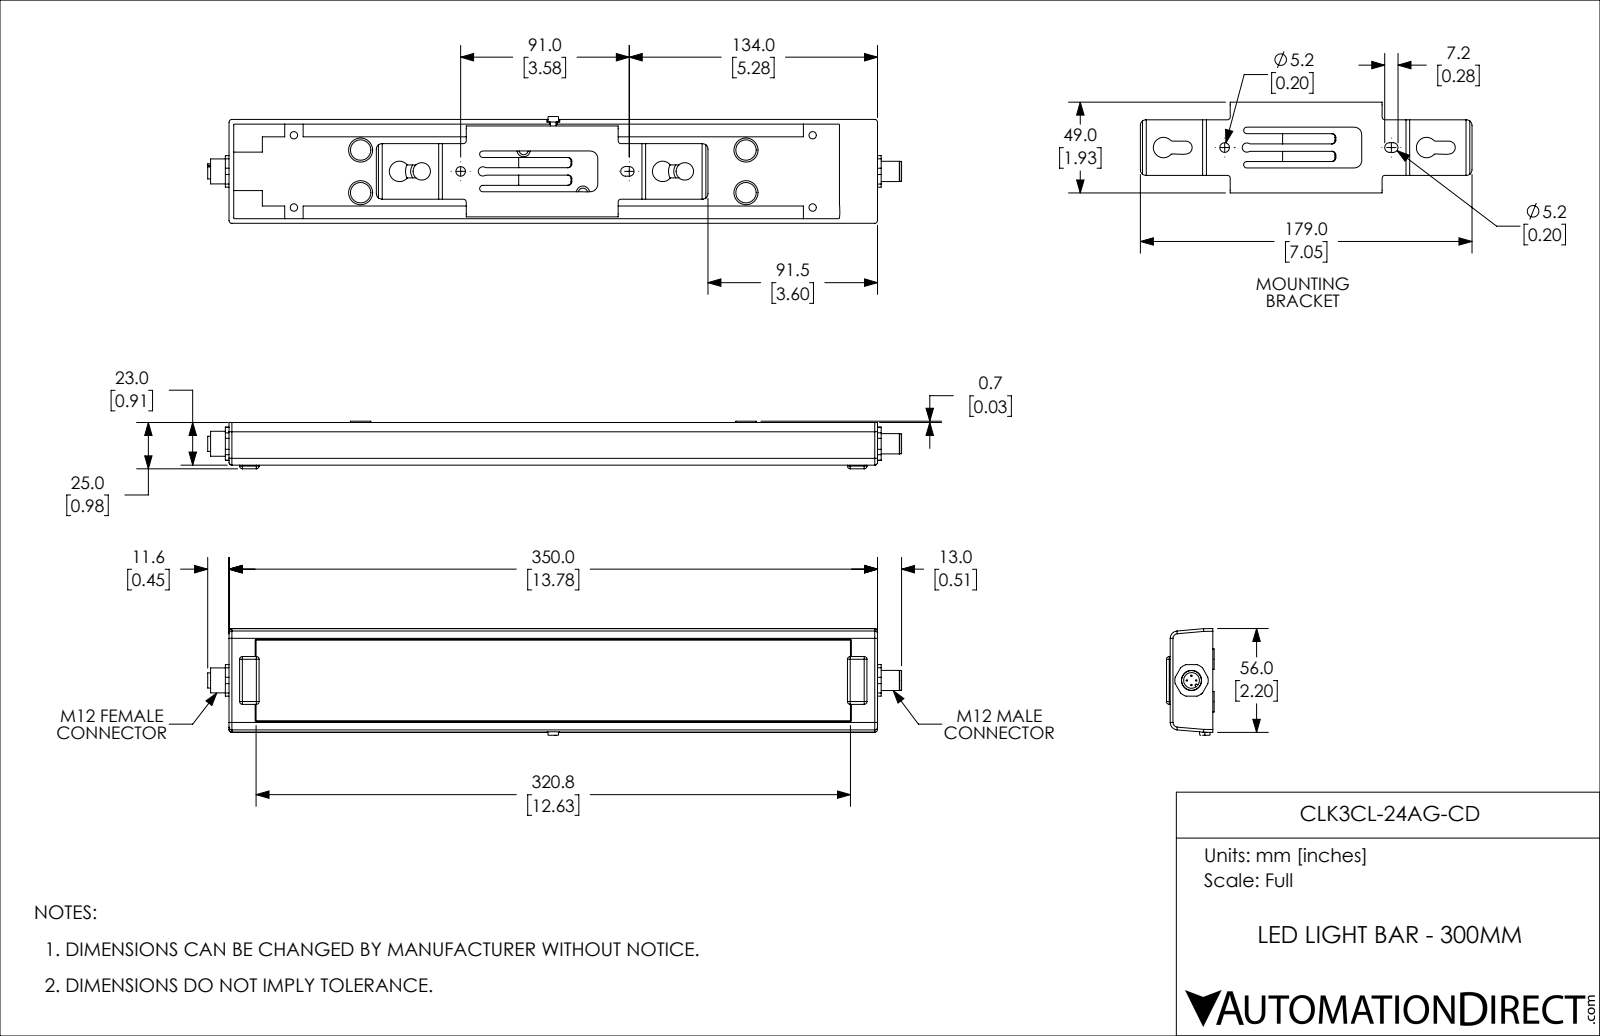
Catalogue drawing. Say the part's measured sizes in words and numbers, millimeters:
The part is named "CLK3CL-24AG-CD". Its 3-D file was written by "SolidWorks 2018 (AUTOMOTIVE_DESIGN)". It is 5 solids with 357 faces: 154 planar, 139 cylindrical and 64 other. Overall it measures 374.55 by 57.6 by 25.7 millimeters. Its volume is 320 663 cubic millimeters and its surface area 96 139 square millimeters. Round holes: 5 of diameter 0.8, 4 of diameter 4, 1 of diameter 3, 1 of diameter 5.2, 1 of diameter 8.5, 1 of diameter 12. Round bosses or shafts: 4 of diameter 13, 4 of diameter 11, 2 of diameter 9.4, 2 of diameter 6.5, 1 of diameter 13.5, 1 of diameter 10.9, 1 of diameter 10.7, 1 of diameter 8.19. Partial cylindrical surfaces (rounded edges, fillets, slot ends): 20 of radius 1.5, 4 of radius 2, 2 of radius 2.6, 2 of radius 3.5, 2 of radius 4, 2 of radius 5.5, 1 of radius 0.6, 1 of radius 9. The main face-to-face distances are 17.7, 1.5, 6.84, 44.16, 3.5, 10.25, 7.45, 51, 22.7, 5. The hole center spacings are 2.5, 3.54, 5, 39, 92.09, 191, 280, 282.7.
